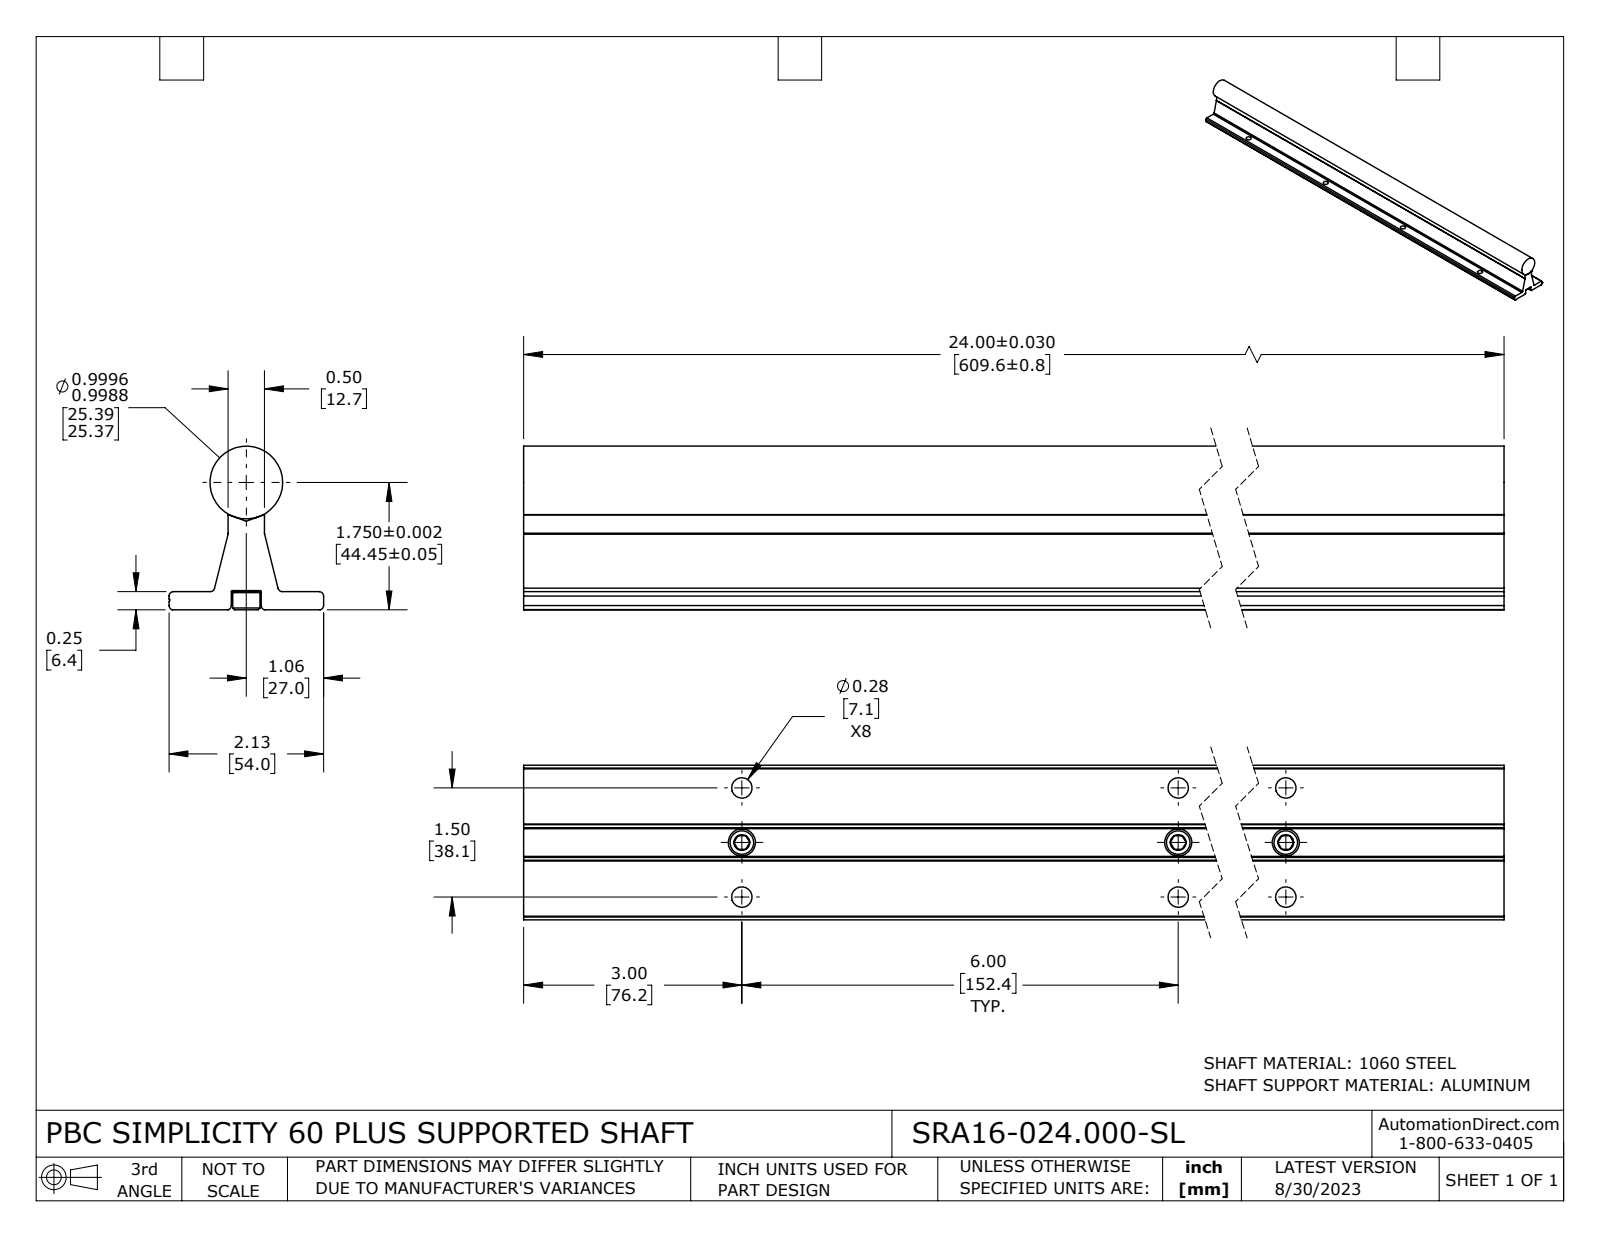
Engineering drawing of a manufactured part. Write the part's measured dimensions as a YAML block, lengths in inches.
part_name: "SRA16-024.000-SL"
step_written_by: "SolidWorks 2021 (CONFIG_CONTROL_DESIGN)"
units: inches
bodies: {solids: 6, faces: 203, planar: 71, cylindrical: 72, other: 60}
overall_size: [24, 2.25, 2.125]
volume: 44.75
surface_area: 257.5
round_holes:
  - {diameter: 0.281, count: 12}
  - {diameter: 0.213, count: 4}
  - {diameter: 0.313, count: 4}
round_bosses_or_shafts:
  - {diameter: 0.375, count: 4}
  - {diameter: 0.25, count: 4}
  - {diameter: 1, count: 1}
partial_cylinders:
  - {radius: 0.06, count: 6}
  - {radius: 0.063, count: 4}
  - {radius: 0.015, count: 2}
  - {radius: 0.032, count: 2}
face_to_face_distances: [0.25, 0.045, 0.455, 0.265, 0.015, 0.5, 0.813, 0.857, 1.268, 1.313]
hole_center_spacings: [6.047, 6, 0.75, 12.023, 6.185, 12, 1.5, 12.093]
